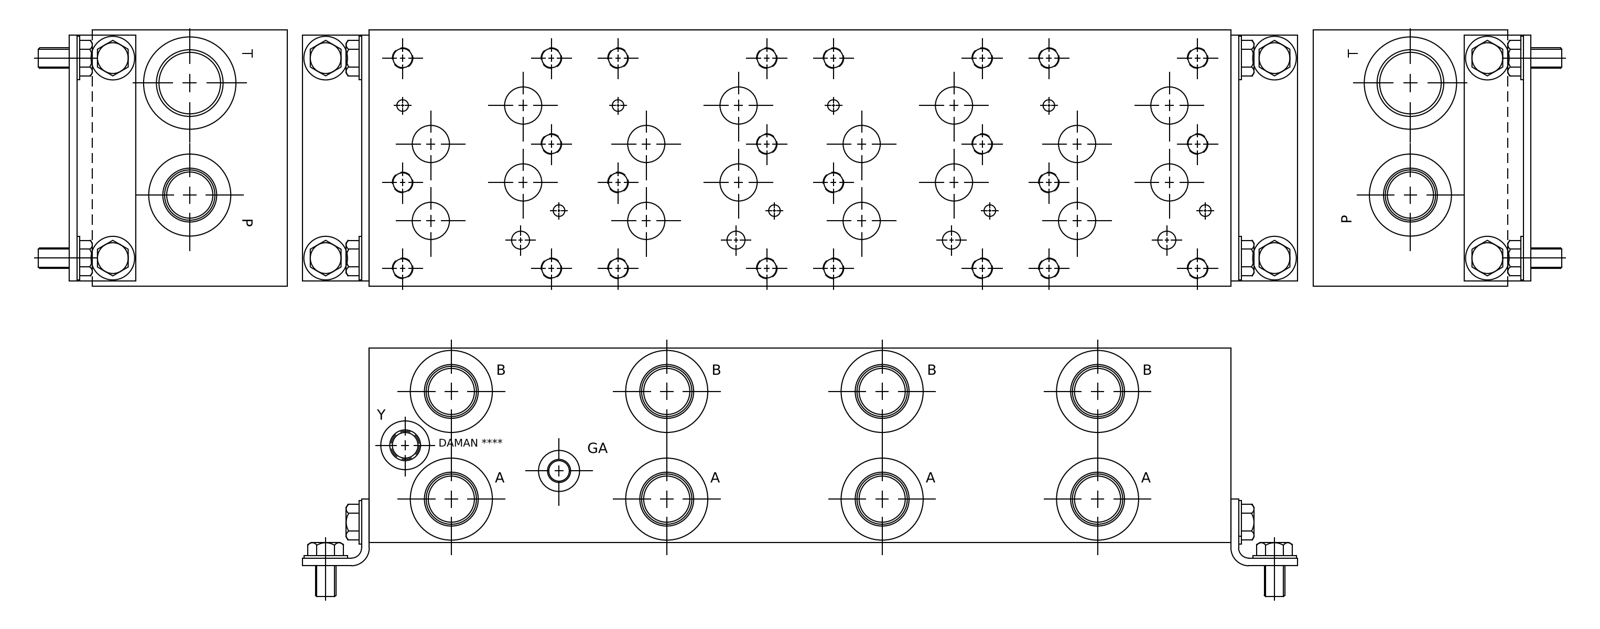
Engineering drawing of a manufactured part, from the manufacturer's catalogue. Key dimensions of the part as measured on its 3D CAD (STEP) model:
Part name (STEP PRODUCT): Part_AD08P045S_3D
STEP written by: Autodesk Inventor 2019 (AUTOMOTIVE_DESIGN)
Units: millimetres
Bodies: 1 solid, 917 faces (445 planar, 162 cylindrical, 310 other)
Overall size (bounding box): 533.4 × 158.75 × 120.65
Volume: 9 622 000 mm³ · Surface area: 435 023 mm²
Round holes (diameter × count): ⌀10.72 ×27, ⌀12.7 ×26, ⌀23.01 ×15, ⌀31.27 ×9, ⌀33.76 ×9, ⌀49.12 ×9, ⌀7.14 ×8, ⌀28.57 ×8, ⌀33.35 ×8, ⌀35.51 ×8, ⌀11.13 ×3, ⌀33.34 ×2
Main face-to-face distances: 120.65, 158.75, 533.4, 0.79, 157.96, 532.61, 531.82, 19.84, 19.05, 90.42
Hole centre spacings: 133.35, 266.7, 191.98, 400.05, 61.92, 270.92, 79.84, 141.6
